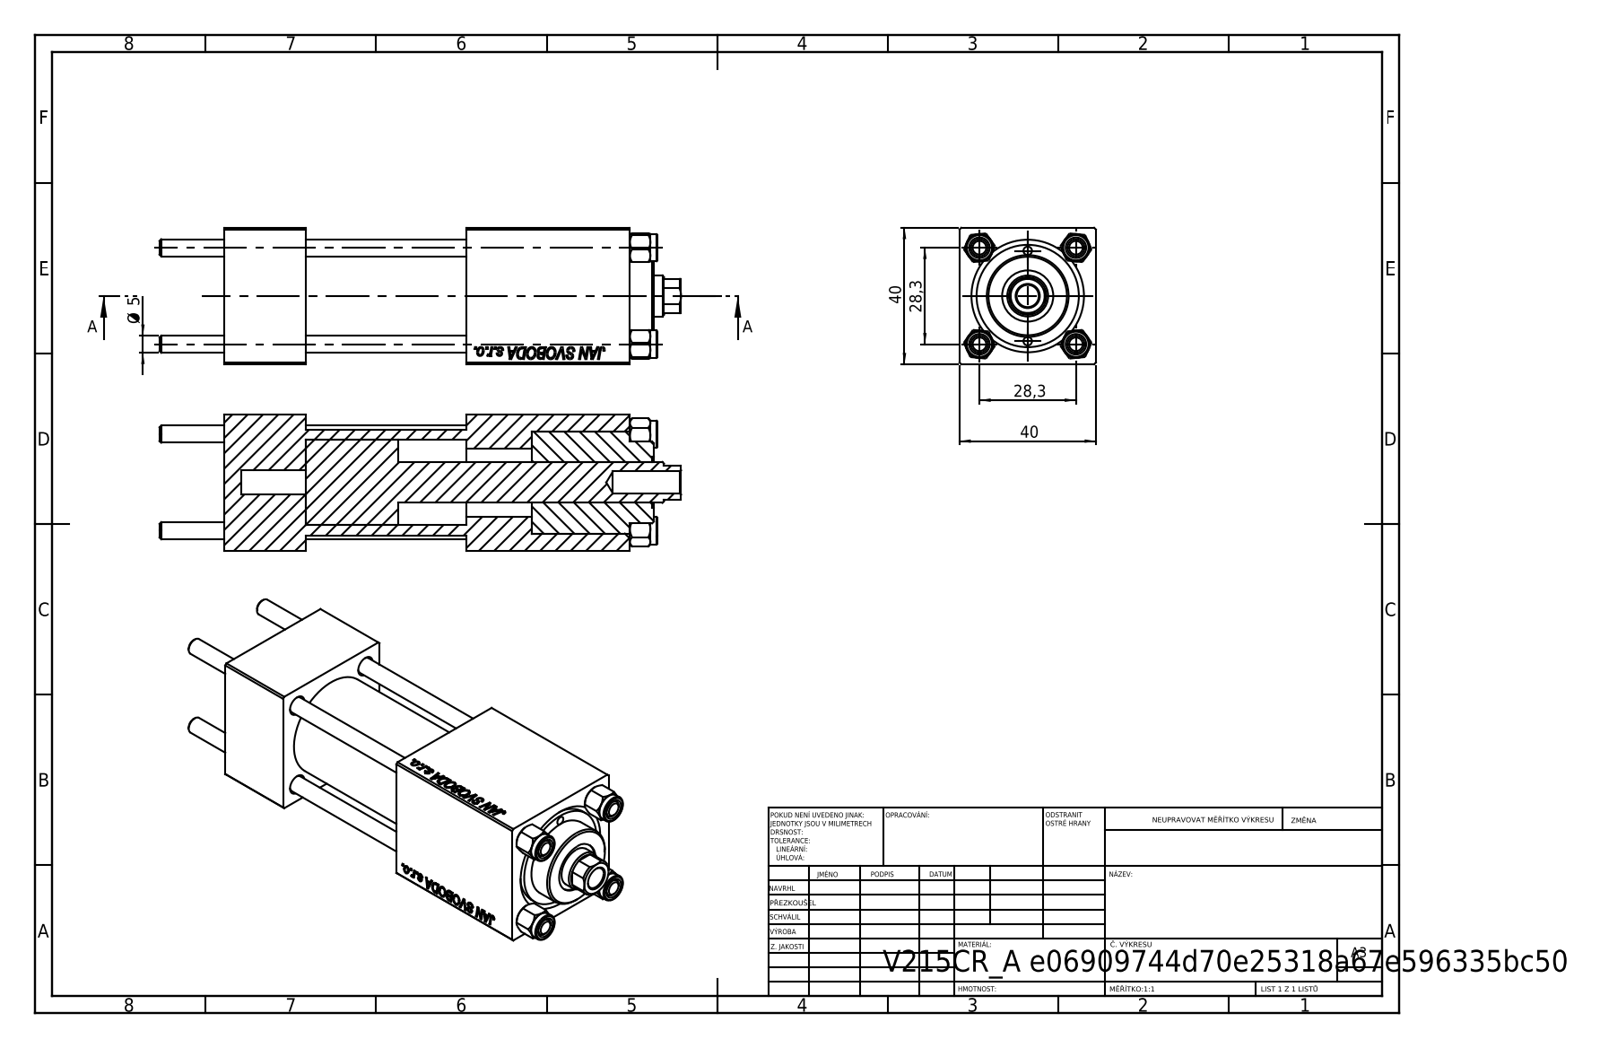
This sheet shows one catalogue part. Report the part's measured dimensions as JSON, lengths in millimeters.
{"part_name": "V215CR_VCP; V215CR_BODY_A; NUT_M5; V215_VC_A (+1 more)", "step_written_by": "SolidWorks 2019 (CONFIG_CONTROL_DESIGN)", "units": "millimeters", "bodies": {"solids": 11, "faces": 1137, "planar": 519, "cylindrical": 82, "other": 536}, "overall_size": [153, 40, 40], "volume_mm3": 144775, "surface_area_mm2": 58950, "round_holes": [[5, 4], [20, 3], [2.5, 2], [7, 2], [13.16, 2], [6.5, 1], [12, 1], [15, 1], [25, 1], [30, 1]], "round_bosses_or_shafts": [[8, 4], [31, 1], [24, 1]], "partial_cylinders_radius": [[5.5, 1]], "face_to_face_distances": [40, 24, 90.3, 66.3, 119, 95, 28.7, 71, 47, 19.3], "hole_center_spacings": [14.18, 20.01, 28.3, 30.84, 13.25, 40.02, 26.5, 72]}
